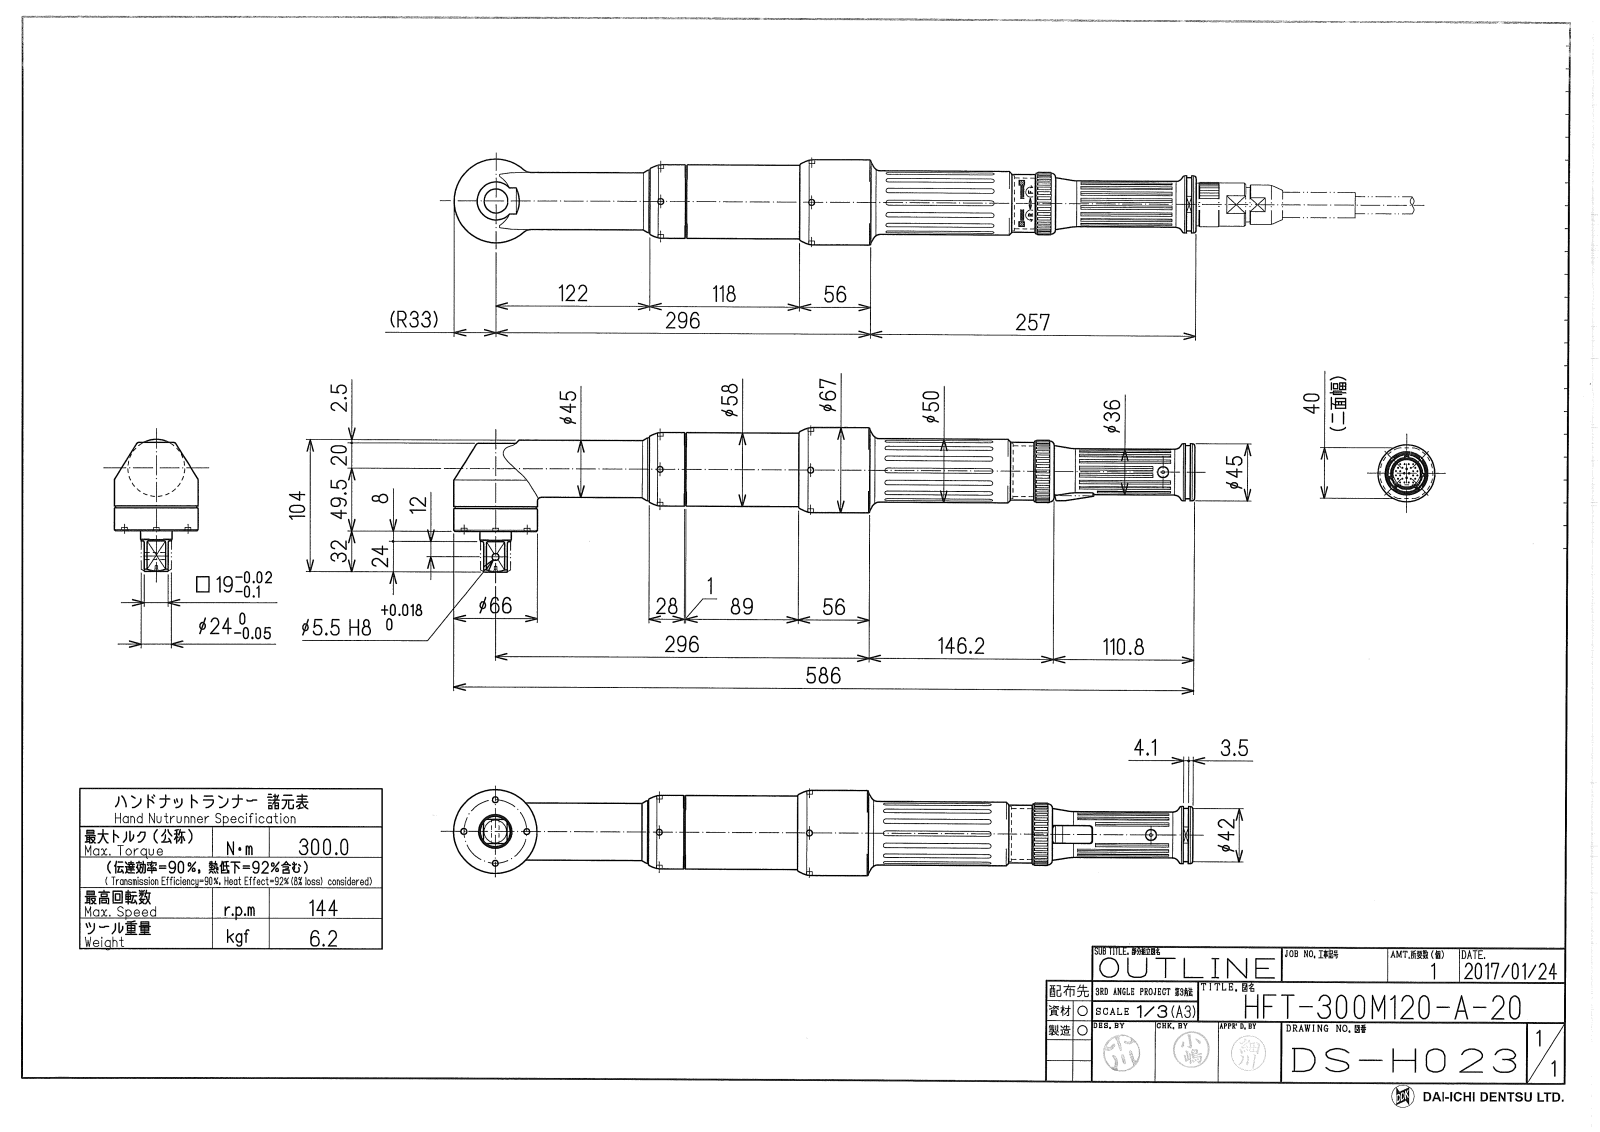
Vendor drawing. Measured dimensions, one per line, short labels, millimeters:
name: HFT-300M120-A-20(DS-H023+A)_OUTLINE
written by: Autodesk Inventor 2017 (AUTOMOTIVE_DESIGN)
unit: mm
bodies: 1 solid, 830 faces (438 planar, 261 cylindrical, 131 other)
size: 586 × 115 × 67
volume: 1 252 000 mm³; area: 117 204 mm²
holes: 8× ⌀4.6, 2× ⌀9, 2× ⌀64.4, 1× ⌀2, 1× ⌀3, 1× ⌀4.5, 1× ⌀5.5, 1× ⌀6, 1× ⌀6.8, 1× ⌀19, 1× ⌀22.6, 1× ⌀25
bosses: 24× ⌀1, 4× ⌀1.6, 2× ⌀64, 2× ⌀8, 1× ⌀67, 1× ⌀66, 1× ⌀58, 1× ⌀56
rounds: 36× R0.1, 36× R1.5, 18× R0.33, 18× R3, 6× R1, 6× R2.5, 2× R0.3, 2× R0.88
face distances: 34.96, 19, 69.5, 1.5, 15.4, 11.9, 2, 67.5, 0.5, 50
hole spacings: 25, 35.36, 50, 119, 132.87, 250.75, 450.99, 461.98
